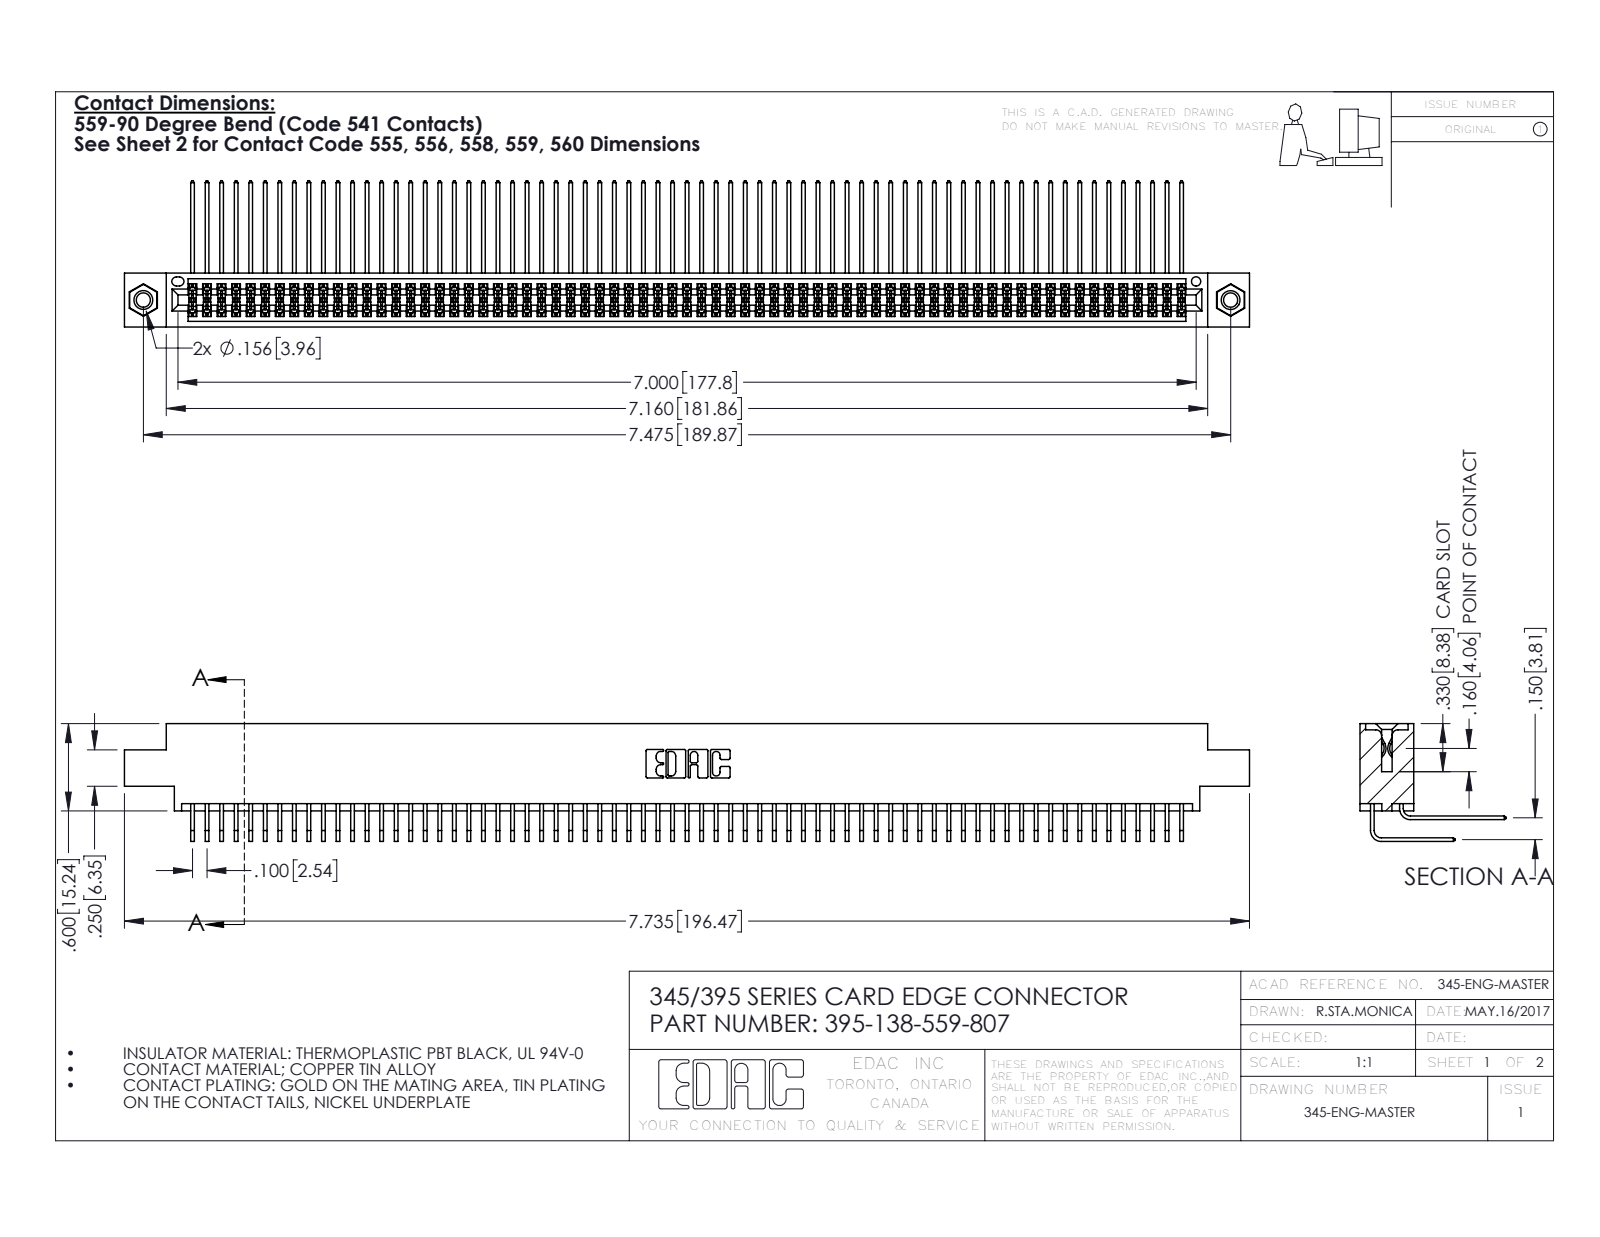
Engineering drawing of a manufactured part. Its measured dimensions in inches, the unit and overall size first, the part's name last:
Units: inches
Overall size (bounding box): 7.735 × 1.005 × 0.809
Round holes (diameter × count): ⌀0.098 ×2, ⌀0.125 ×2, ⌀0.156 ×2, ⌀0.064 ×1
Round bosses / shafts (diameter × count): ⌀0.155 ×2
Partial cylindrical surfaces — rounded edges, fillets, slot ends (radius × count): R0.006 ×275, R0.01 ×22, R0.007 ×6, R0.031 ×6, R0.026 ×3, R0.014 ×2, R0.019 ×2, R0.022 ×2
Main face-to-face distances: 0.072, 0.298, 0.2, 0.37, 0.098, 0.272, 0.025, 0.225, 0.175, 0.15
Hole centre spacings: 0.27, 7.239, 7.475
Volume: 1.221 in³ · Surface area: 52.71 in²
Bodies: 141 solids, 7366 faces (4946 planar, 2404 cylindrical, 16 other)
Part name (STEP PRODUCT): 345 Part_0.170 Offset - 0.156 Dia-TI; 345-292-001_558 559 Tail - 1; 395-138-559-807; 345-250-001_345-250-005-103 (+1 more)
STEP written by: SolidWorks 2016 (CONFIG_CONTROL_DESIGN)
